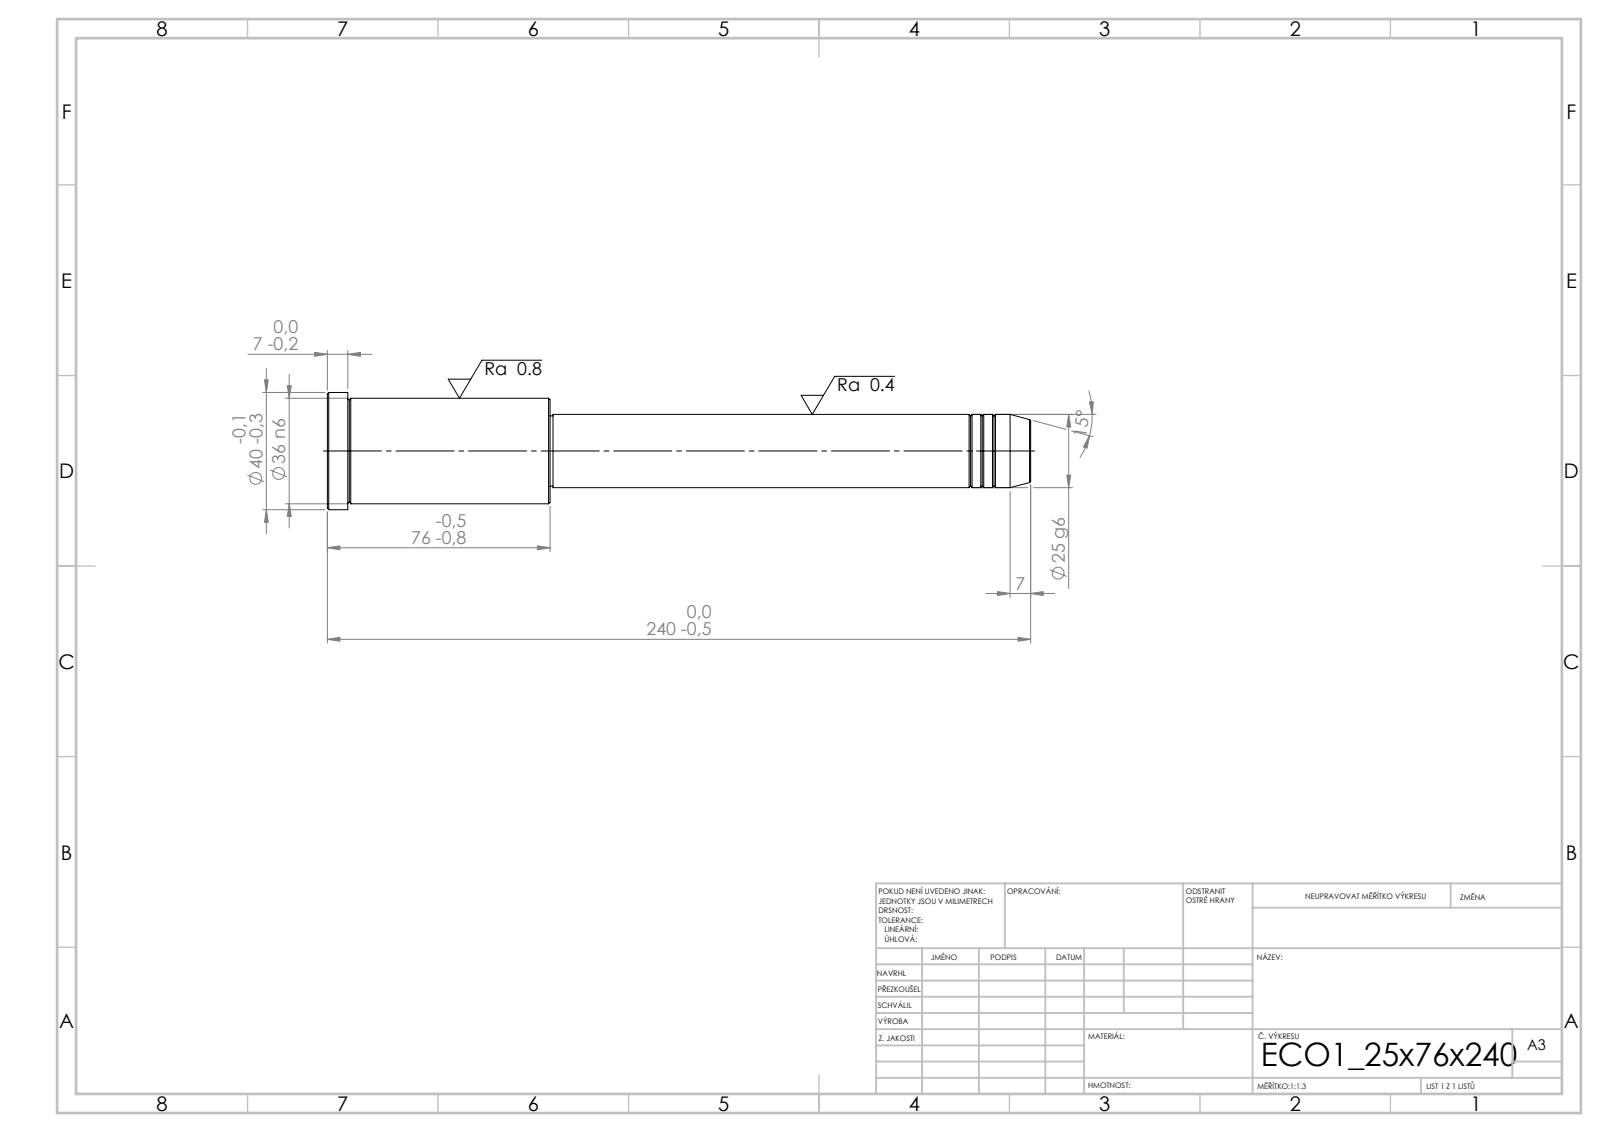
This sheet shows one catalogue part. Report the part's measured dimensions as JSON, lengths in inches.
{"step_written_by": "SolidWorks 2019 (CONFIG_CONTROL_DESIGN)", "units": "inches", "bodies": {"solids": 1, "faces": 43, "planar": 5, "cylindrical": 14, "other": 24}, "overall_size": [9.449, 1.575, 1.575], "volume_in3": 9.693, "surface_area_in2": 37.36, "round_bosses_or_shafts": [[1.575, 1], [1.417, 1], [0.984, 1], [0.945, 1]], "face_to_face_distances": [2.992, 6.457, 9.449, 9.173, 2.717, 0.276, 6.417, 0.039, 2.756, 3.031]}
